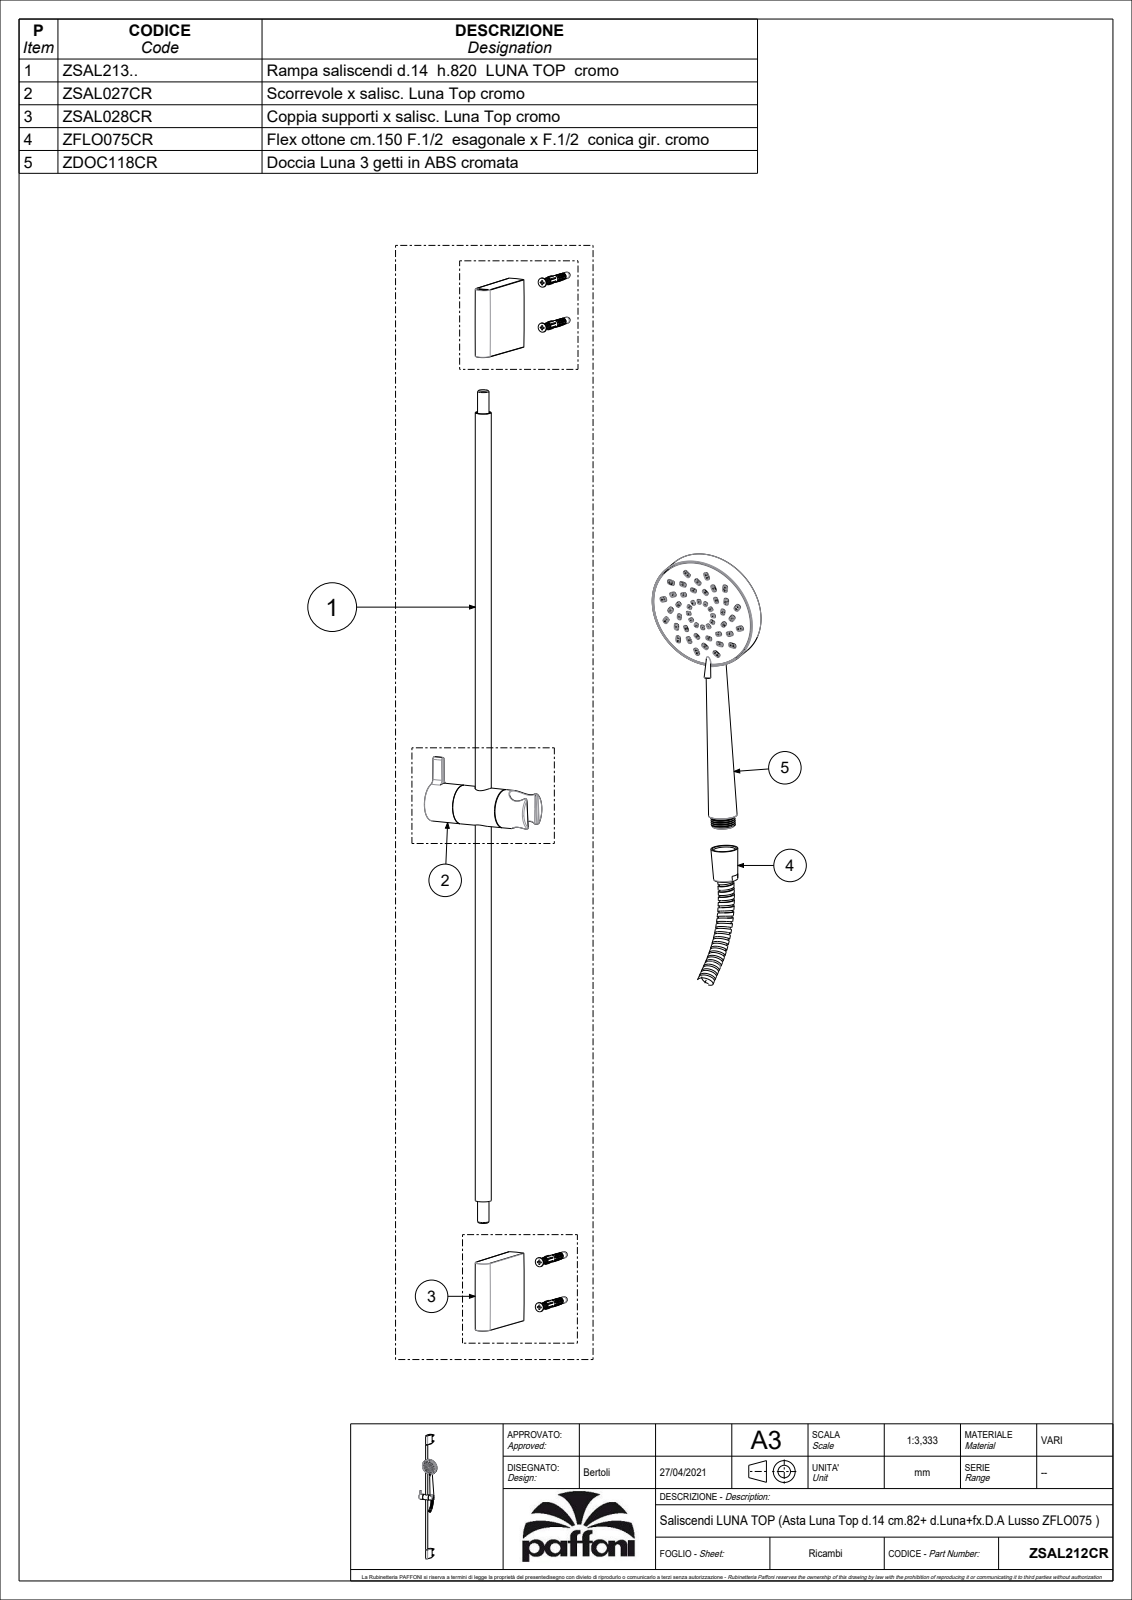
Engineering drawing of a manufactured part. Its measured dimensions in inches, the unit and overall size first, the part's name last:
Units: inches
Overall size (bounding box): 32.299 × 5.543 × 4.288
Round holes (diameter × count): ⌀0.102 ×48, ⌀0.087 ×12, ⌀0.236 ×5, ⌀0.126 ×2, ⌀0.079 ×1, ⌀0.177 ×1, ⌀0.315 ×1, ⌀0.394 ×1, ⌀0.472 ×1, ⌀0.492 ×1, ⌀0.551 ×1, ⌀0.571 ×1
Round bosses / shafts (diameter × count): ⌀1.22 ×2, ⌀0.354 ×2, ⌀3.937 ×1, ⌀3.819 ×1, ⌀3.488 ×1, ⌀1.457 ×1, ⌀1.339 ×1, ⌀0.846 ×1
Partial cylindrical surfaces — rounded edges, fillets, slot ends (radius × count): R0.02 ×81, R0.025 ×48, R0.029 ×48, R0.031 ×48, R0.033 ×48, R0.051 ×48, R0.043 ×36, R0.048 ×36
Main face-to-face distances: 0.099, 0.489, 0.587, 0.02, 0.047, 2.409, 0.224, 0.469, 0.568, 0.111
Hole centre spacings: 0.483, 0.933, 0.837, 0.483, 0.683, 0.25, 0.25, 0.441
Volume: 12.73 in³ · Surface area: 318.9 in²
Bodies: 8 solids, 4801 faces (545 planar, 1224 cylindrical, 3032 other)
Part name (STEP PRODUCT): 4072126CR_A; 4072126CR_F; 4072126CR_B; 4072127CR (+8 more)
STEP written by: CREO PARAMETRIC BY PTC INC, 2020044 (CONFIG_CONTROL_DESIGN)
